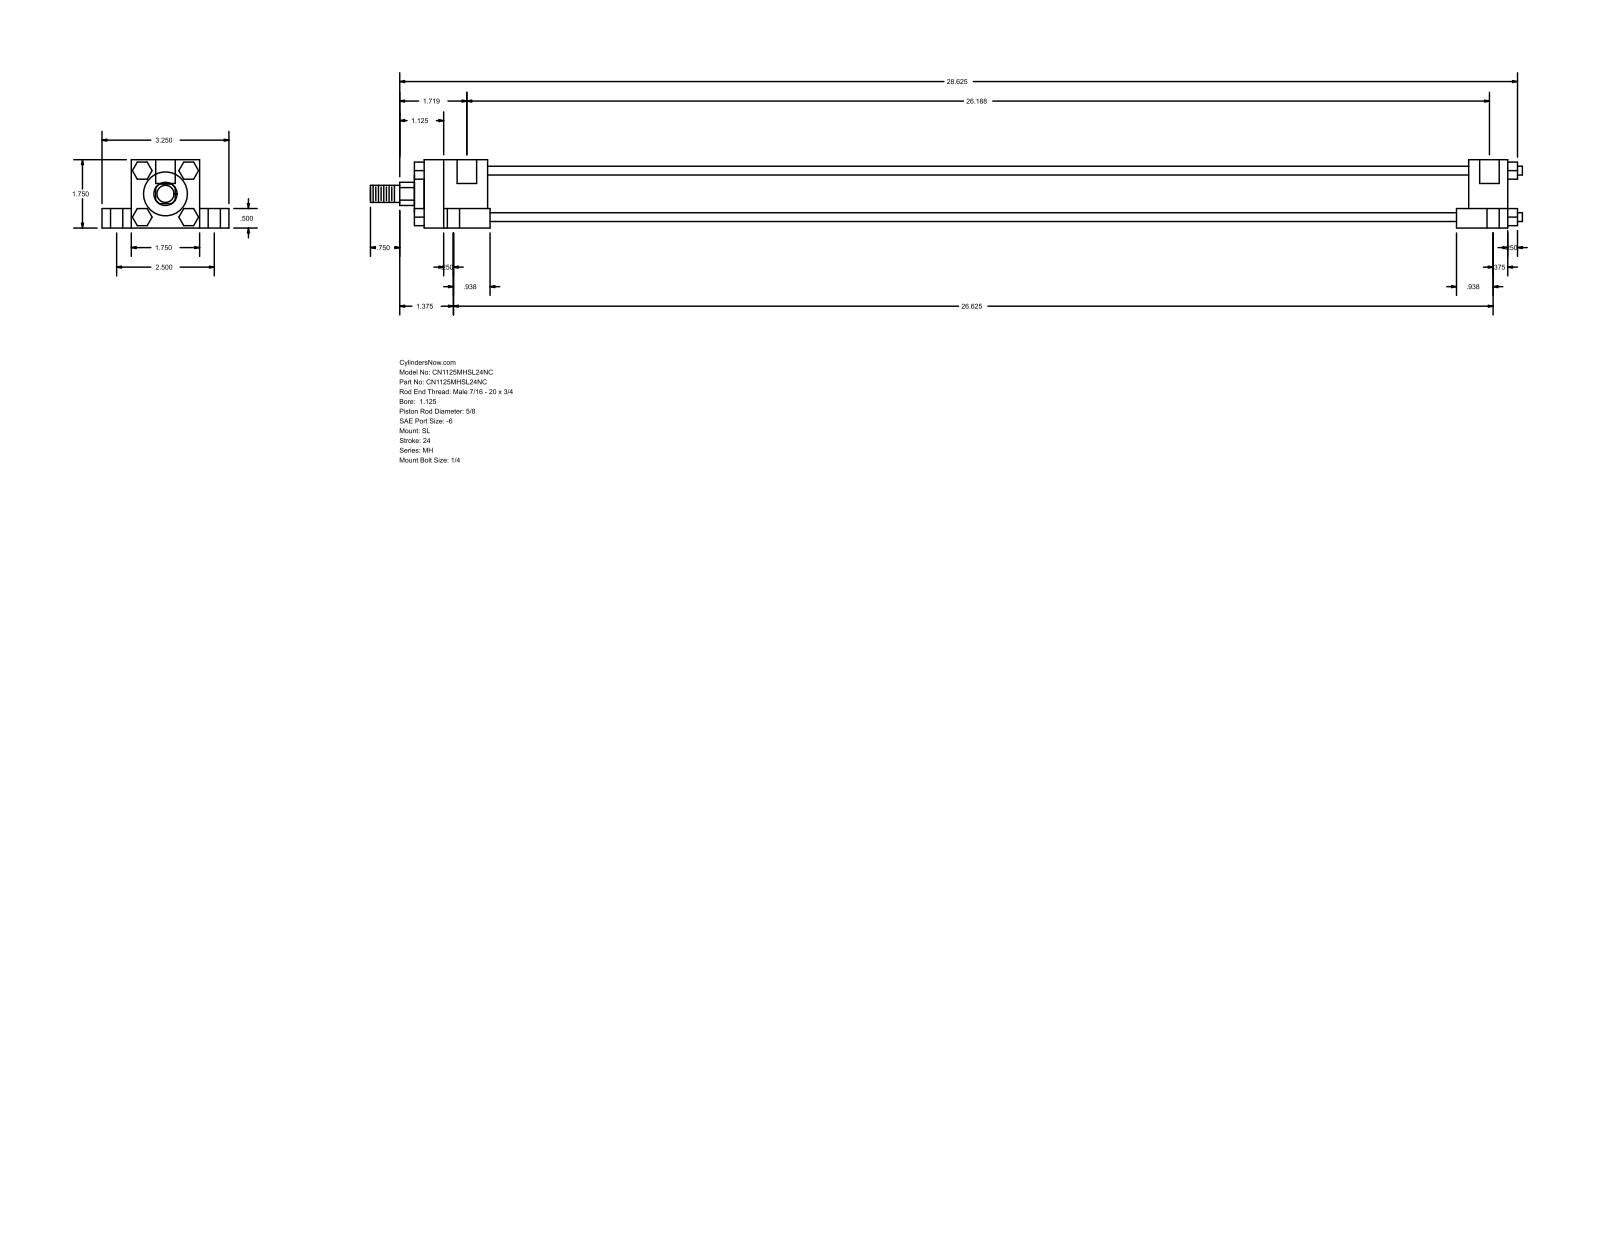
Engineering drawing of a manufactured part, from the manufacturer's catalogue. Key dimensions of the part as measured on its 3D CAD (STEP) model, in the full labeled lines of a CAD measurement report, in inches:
Part name (STEP PRODUCT): MH_SL__0112_0.625
STEP written by: GSSL Pune (CONFIG_CONTROL_DESIGN)
Units: inches
Bodies: 0 solids, 150 faces (114 planar, 36 cylindrical, 0 other)
Overall size (bounding box): 29.5 × 3.25 × 1.75
Round holes (diameter × count): ⌀0.219 ×4, ⌀0.313 ×4, ⌀0.563 ×4, ⌀0.5 ×2
Round bosses / shafts (diameter × count): ⌀0.225 ×4, ⌀1.375 ×1, ⌀1.125 ×1, ⌀0.625 ×1, ⌀0.437 ×1
Partial cylindrical surfaces — rounded edges, fillets, slot ends (radius × count): R0.297 ×1
Main face-to-face distances: 1.75, 0.75, 0.5, 1.25, 2.5, 0.25, 28, 0.437, 1.875, 1.313
Hole centre spacings: 1.254, 1.269, 1.296, 2.5, 26.063, 26.186, 26.311, 26.436
